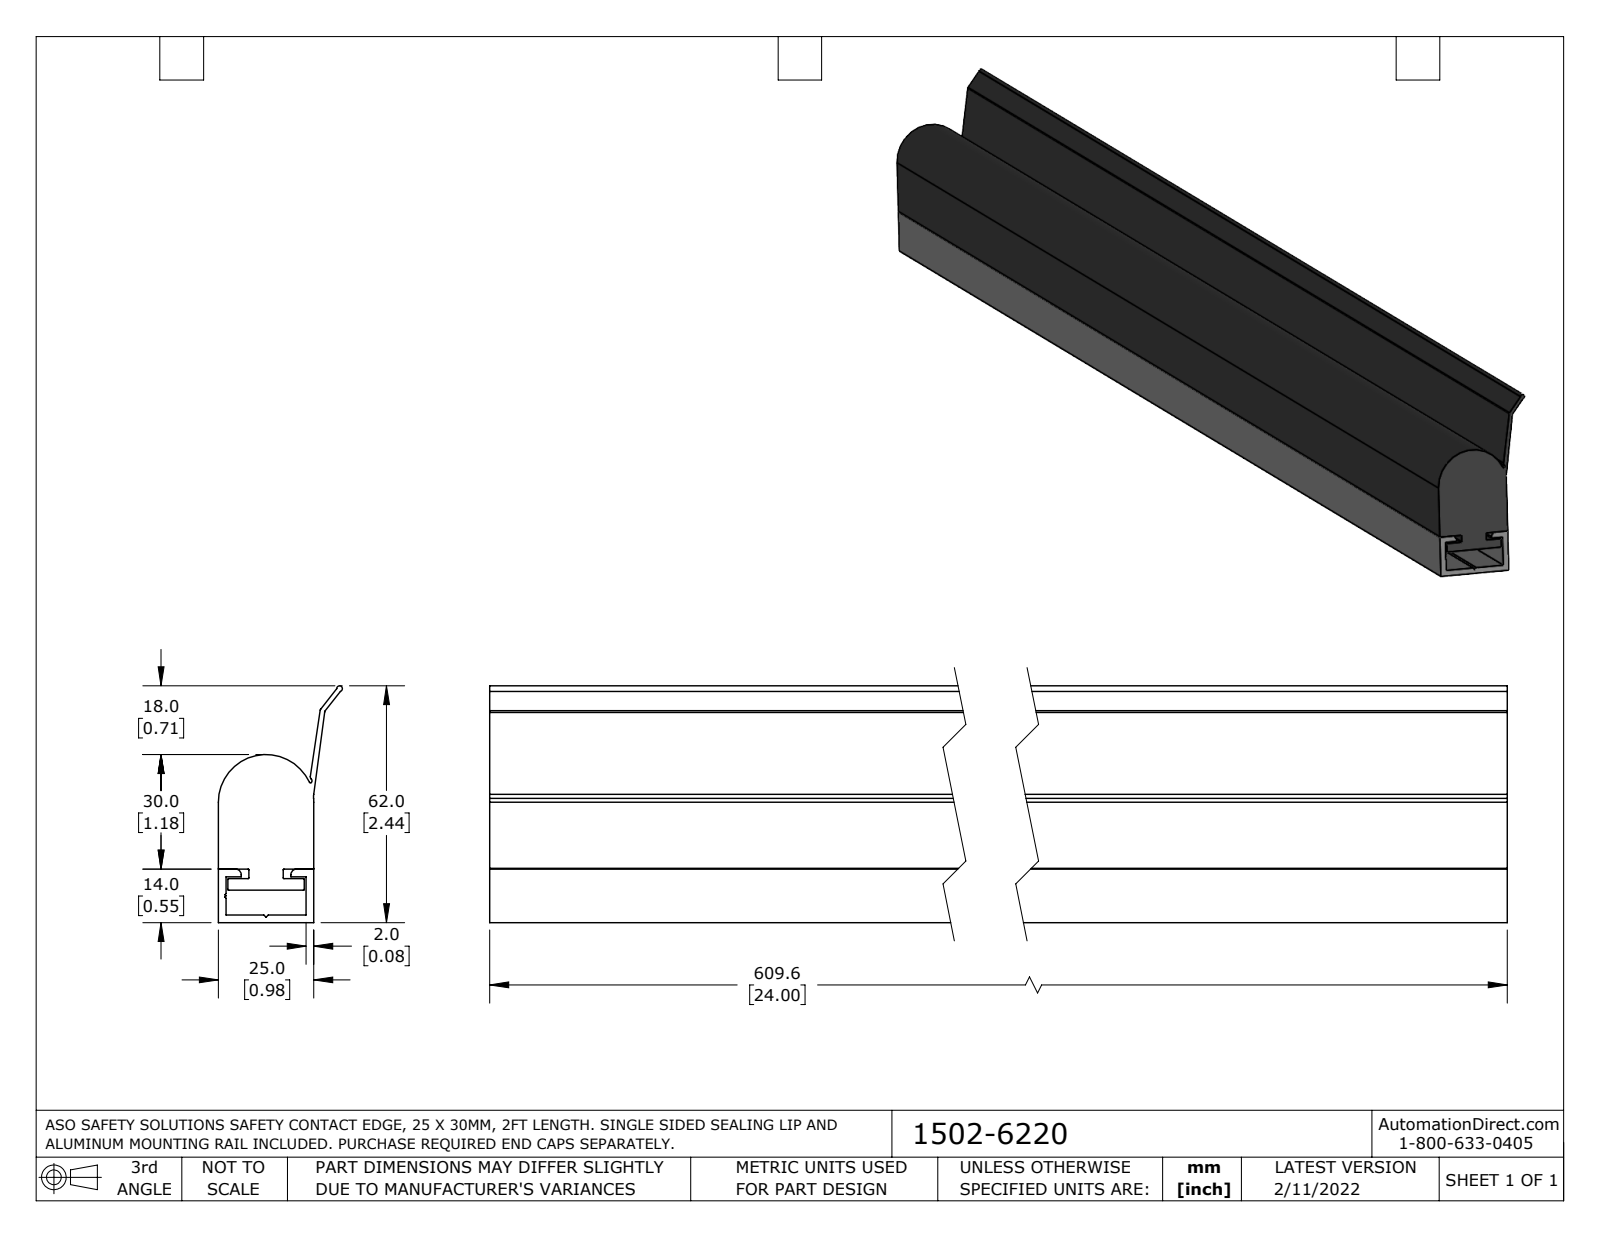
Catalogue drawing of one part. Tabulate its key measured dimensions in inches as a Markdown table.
| quantity | value |
| --- | --- |
| part name | 1502-6220 |
| STEP written by | SolidWorks 2021 (AUTOMOTIVE_DESIGN) |
| units | inches |
| bodies | 2 solids, 61 faces (39 planar, 22 cylindrical, 0 other) |
| overall size | 24 × 2.441 × 1.28 |
| volume | 34.04 in³ |
| surface area | 290.7 in² |
| partial cylindrical surfaces (radius × count) | 0.008 × 10, 0.024 × 2, 0.059 × 2, 0.012 × 1, 0.03 × 1, 0.031 × 1, 0.039 × 1, 0.197 × 1 |
| main face-to-face distances | 0.079, 0.984, 0.472, 0.551, 0.217, 0.335, 0.256, 0.906, 0.098, 0.02 |
